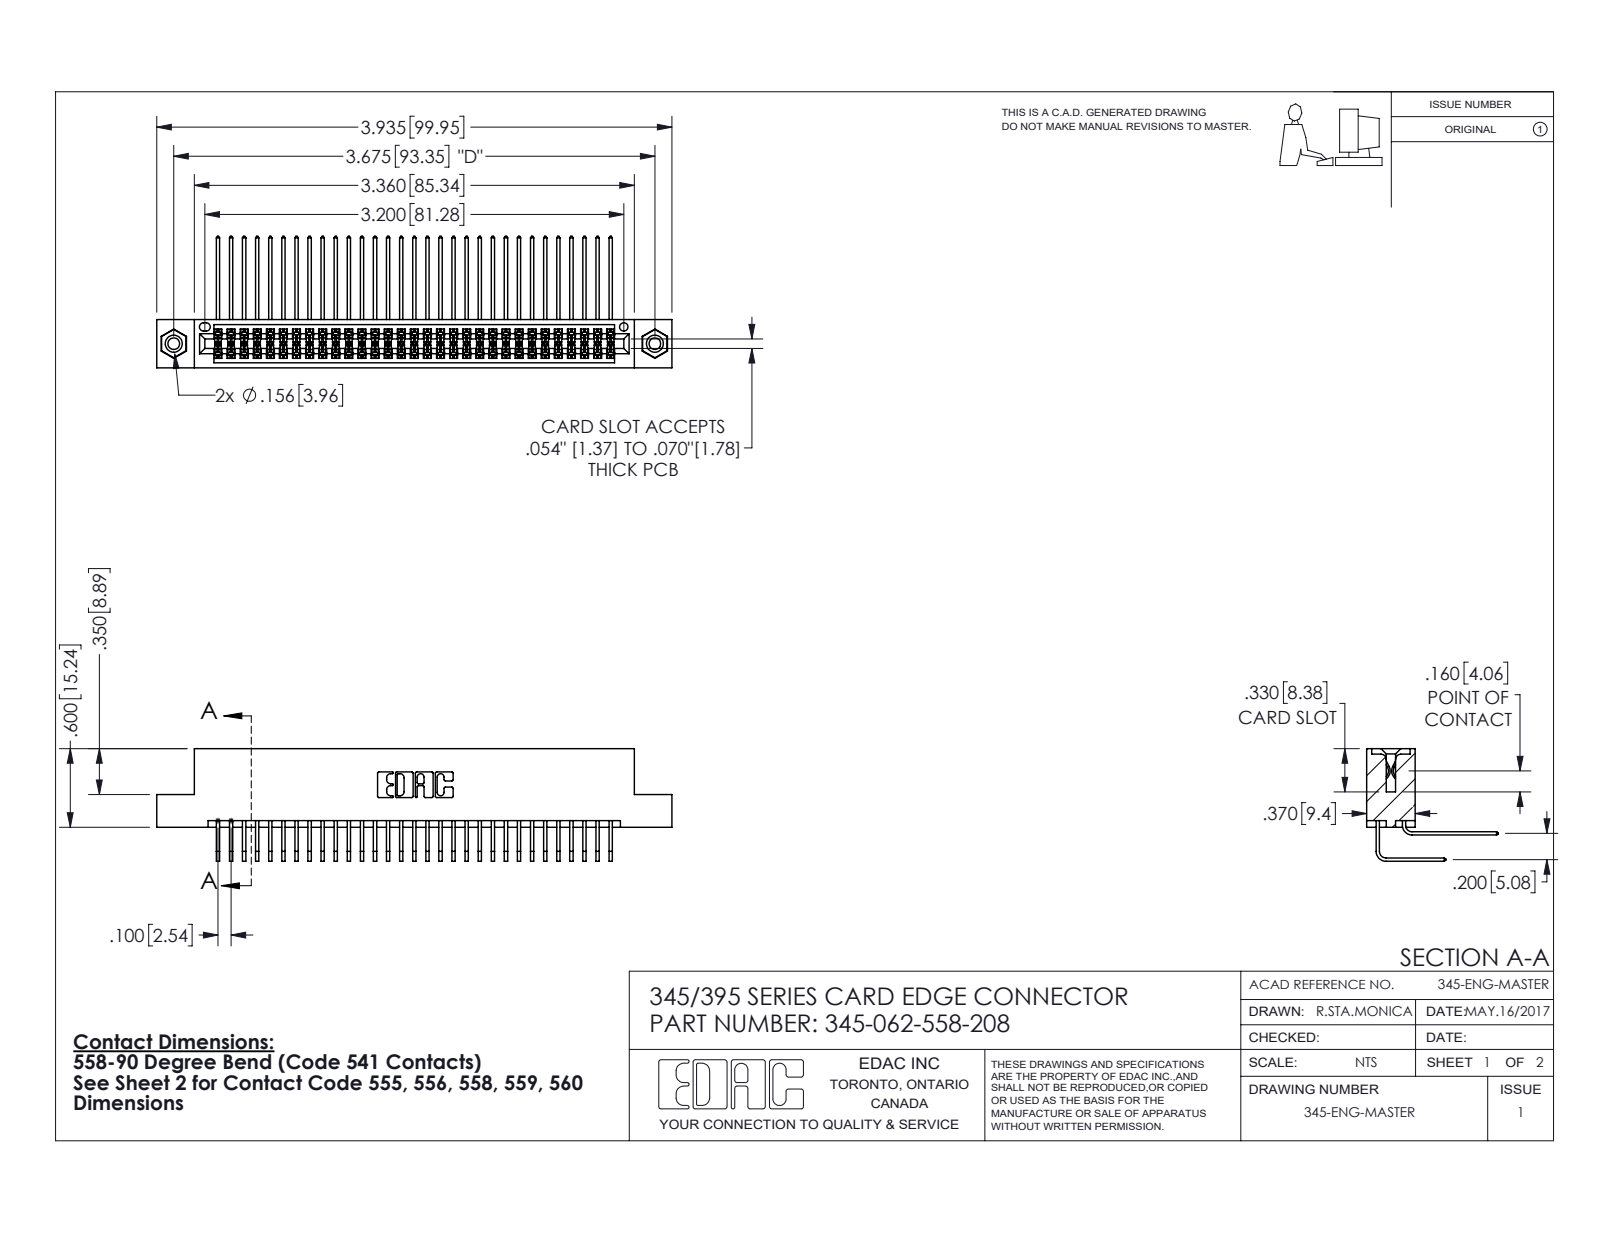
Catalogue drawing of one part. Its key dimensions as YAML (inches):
part_name: "345-062-558-208; 345-292-001_558 Tail - 2; 345 Part_Flush Mounting Lugs - 0.156 Dia-TI; 345-250-001_345-250-003-102 (+1 more)"
step_written_by: "SolidWorks 2016 (CONFIG_CONTROL_DESIGN)"
units: inches
bodies: {solids: 65, faces: 3410, planar: 2282, cylindrical: 1112, other: 16}
overall_size: [3.935, 1.005, 0.859]
volume: 0.608
surface_area: 25.11
round_holes:
  - {diameter: 0.089, count: 2}
  - {diameter: 0.125, count: 2}
  - {diameter: 0.156, count: 2}
  - {diameter: 0.064, count: 1}
round_bosses_or_shafts:
  - {diameter: 0.155, count: 2}
partial_cylinders:
  - {radius: 0.006, count: 124}
  - {radius: 0.01, count: 22}
  - {radius: 0.007, count: 6}
  - {radius: 0.031, count: 6}
  - {radius: 0.026, count: 3}
  - {radius: 0.014, count: 2}
  - {radius: 0.019, count: 2}
  - {radius: 0.022, count: 2}
face_to_face_distances: [0.2, 0.072, 0.298, 0.37, 0.098, 0.272, 0.025, 0.225, 0.025, 0.175]
hole_center_spacings: [0.27, 3.44, 3.675]
